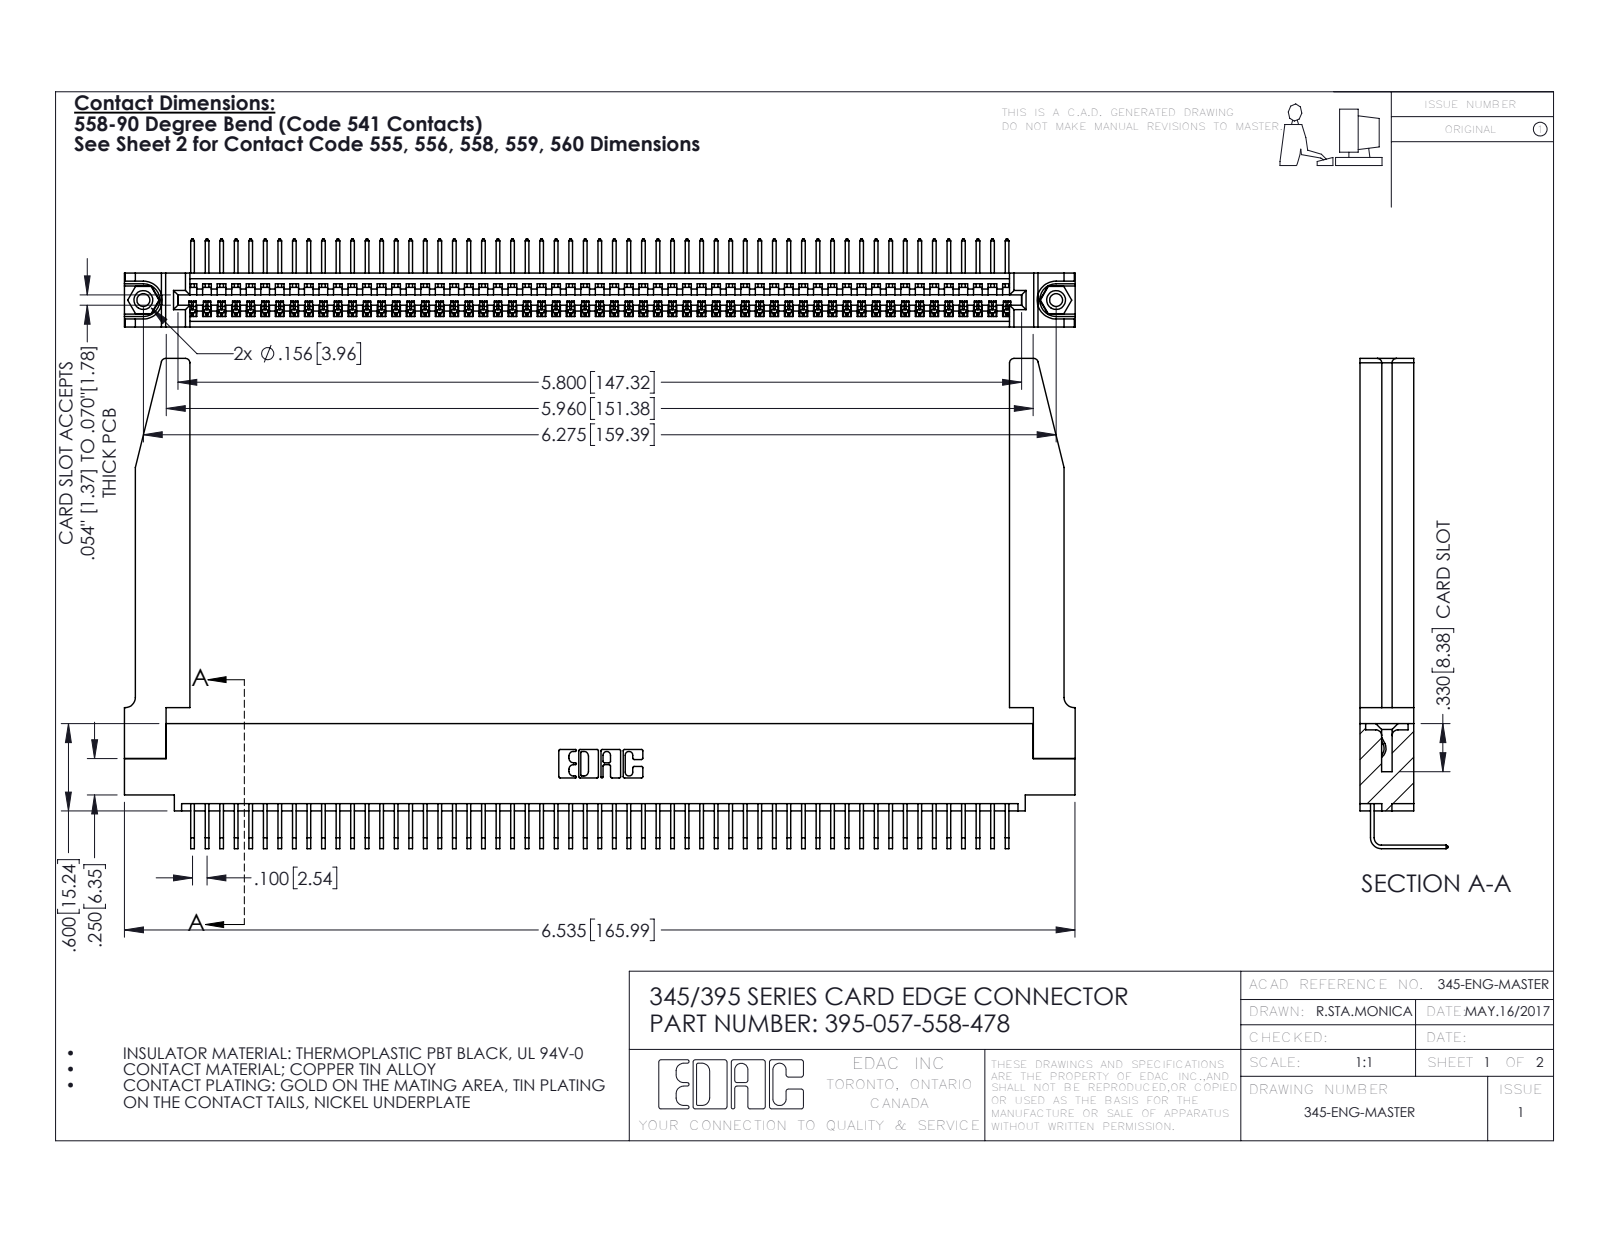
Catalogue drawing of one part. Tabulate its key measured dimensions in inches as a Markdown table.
| quantity | value |
| --- | --- |
| part name | 345-292-001_558 Tail - 2; 345 Part_0.110 Offset - 0.156 Dia-TH; 345-220-078_345-220-078; 395-057-558-478 (+1 more) |
| STEP written by | SolidWorks 2016 (CONFIG_CONTROL_DESIGN) |
| units | inches |
| bodies | 62 solids, 3784 faces (2620 planar, 1112 cylindrical, 52 other) |
| overall size | 6.536 × 3.369 × 0.605 |
| volume | 1.451 in³ |
| surface area | 45.76 in² |
| round holes (diameter × count) | 0.089 × 2, 0.125 × 2, 0.156 × 2, 0.064 × 1 |
| round bosses / shafts (diameter × count) | 0.155 × 2 |
| partial cylindrical surfaces (radius × count) | 0.006 × 114, 0.01 × 22, 0.03 × 8, 0.007 × 6, 0.031 × 6, 0.026 × 3, 0.031 × 2, 0.04 × 2 |
| main face-to-face distances | 0.37, 0.072, 0.298, 0.2, 0.098, 0.272, 0.025, 0.225, 0.148, 0.15 |
| hole center spacings | 0.27, 6.039, 6.275 |
